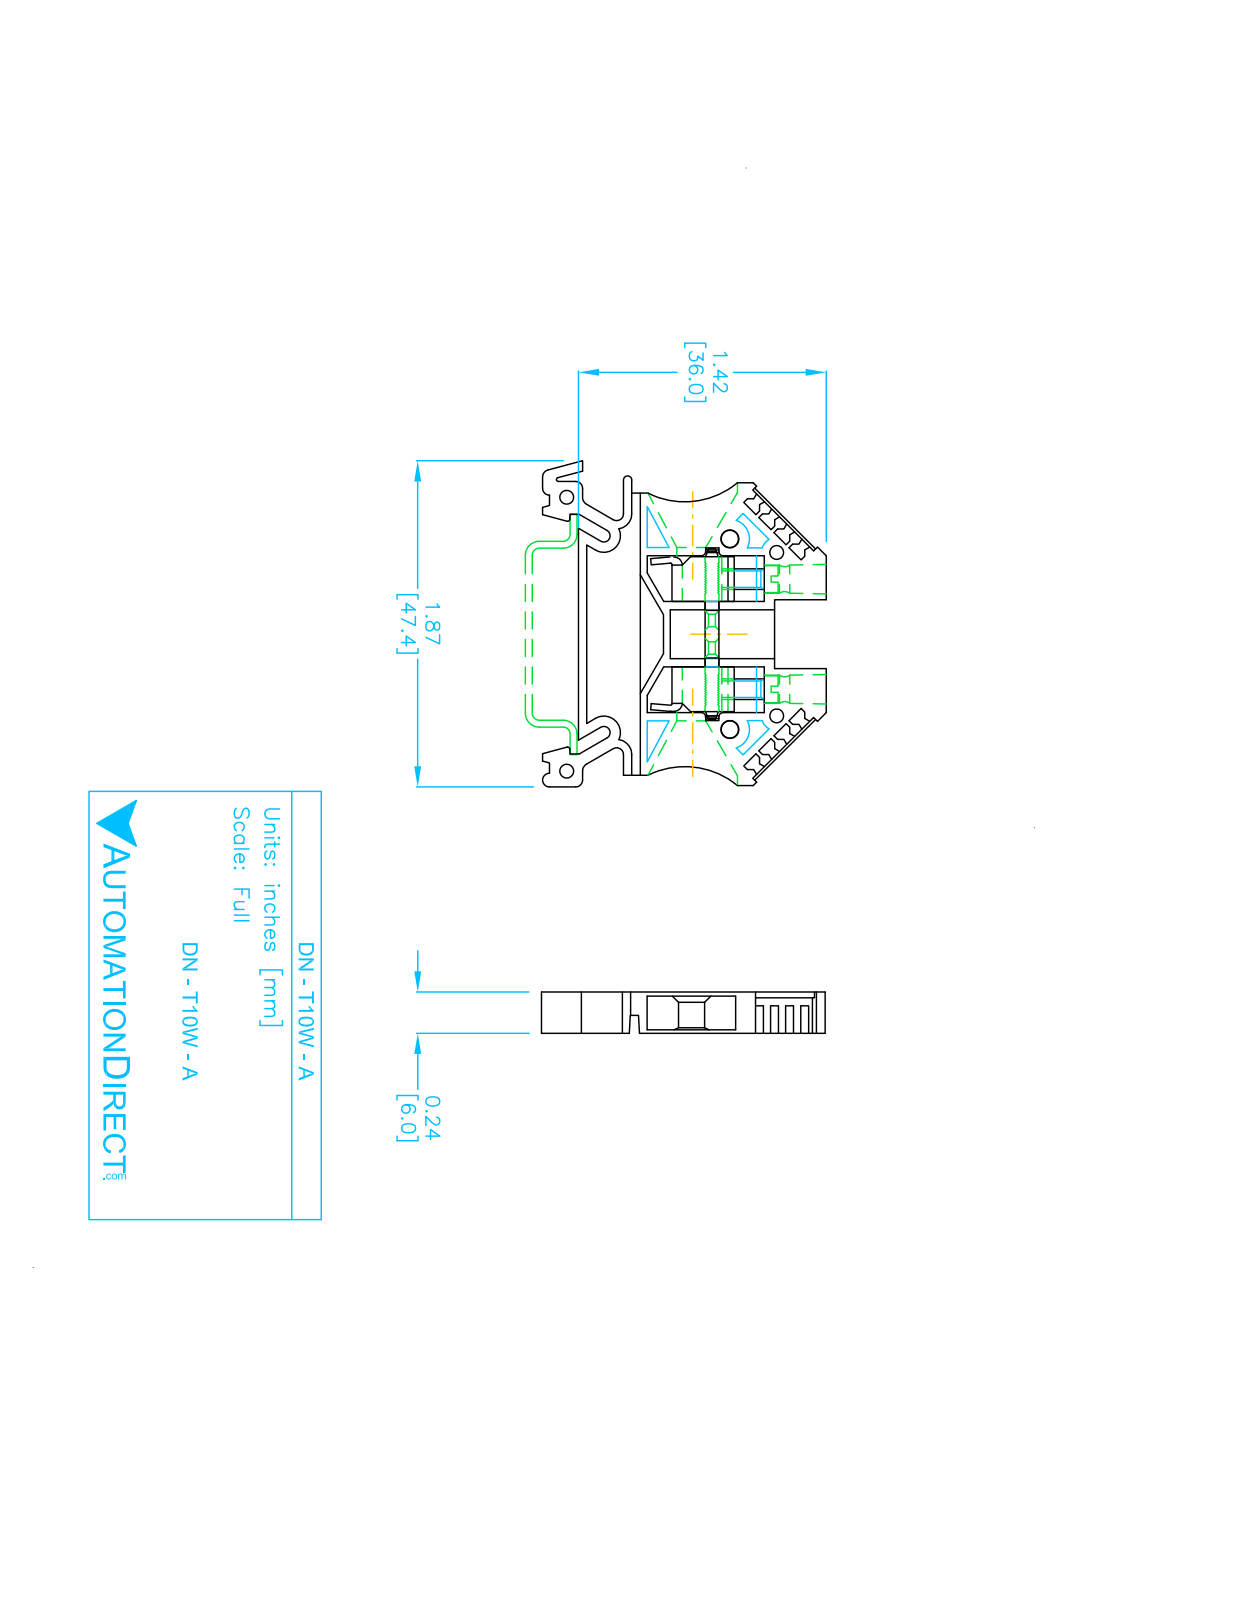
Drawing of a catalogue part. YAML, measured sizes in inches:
part_name: "DN-T10W-A"
step_written_by: "SolidWorks 2017 (AUTOMOTIVE_DESIGN)"
units: inches
bodies: {solids: 1, faces: 181, planar: 141, cylindrical: 40, other: 0}
overall_size: [1.866, 1.622, 0.236]
volume: 0.381
surface_area: 7.683
round_holes:
  - {diameter: 0.079, count: 2}
  - {diameter: 0.172, count: 2}
partial_cylinders:
  - {radius: 0.039, count: 7}
  - {radius: 0.012, count: 2}
  - {radius: 0.035, count: 2}
  - {radius: 0.047, count: 2}
  - {radius: 0.087, count: 2}
  - {radius: 0.094, count: 2}
  - {radius: 0.472, count: 2}
  - {radius: 0.011, count: 1}
face_to_face_distances: [0.228, 0.236, 0.142, 0.094, 0.047, 0.087, 0.134, 0.354, 0.071, 0.307]
hole_center_spacings: [0.63, 1.567]
